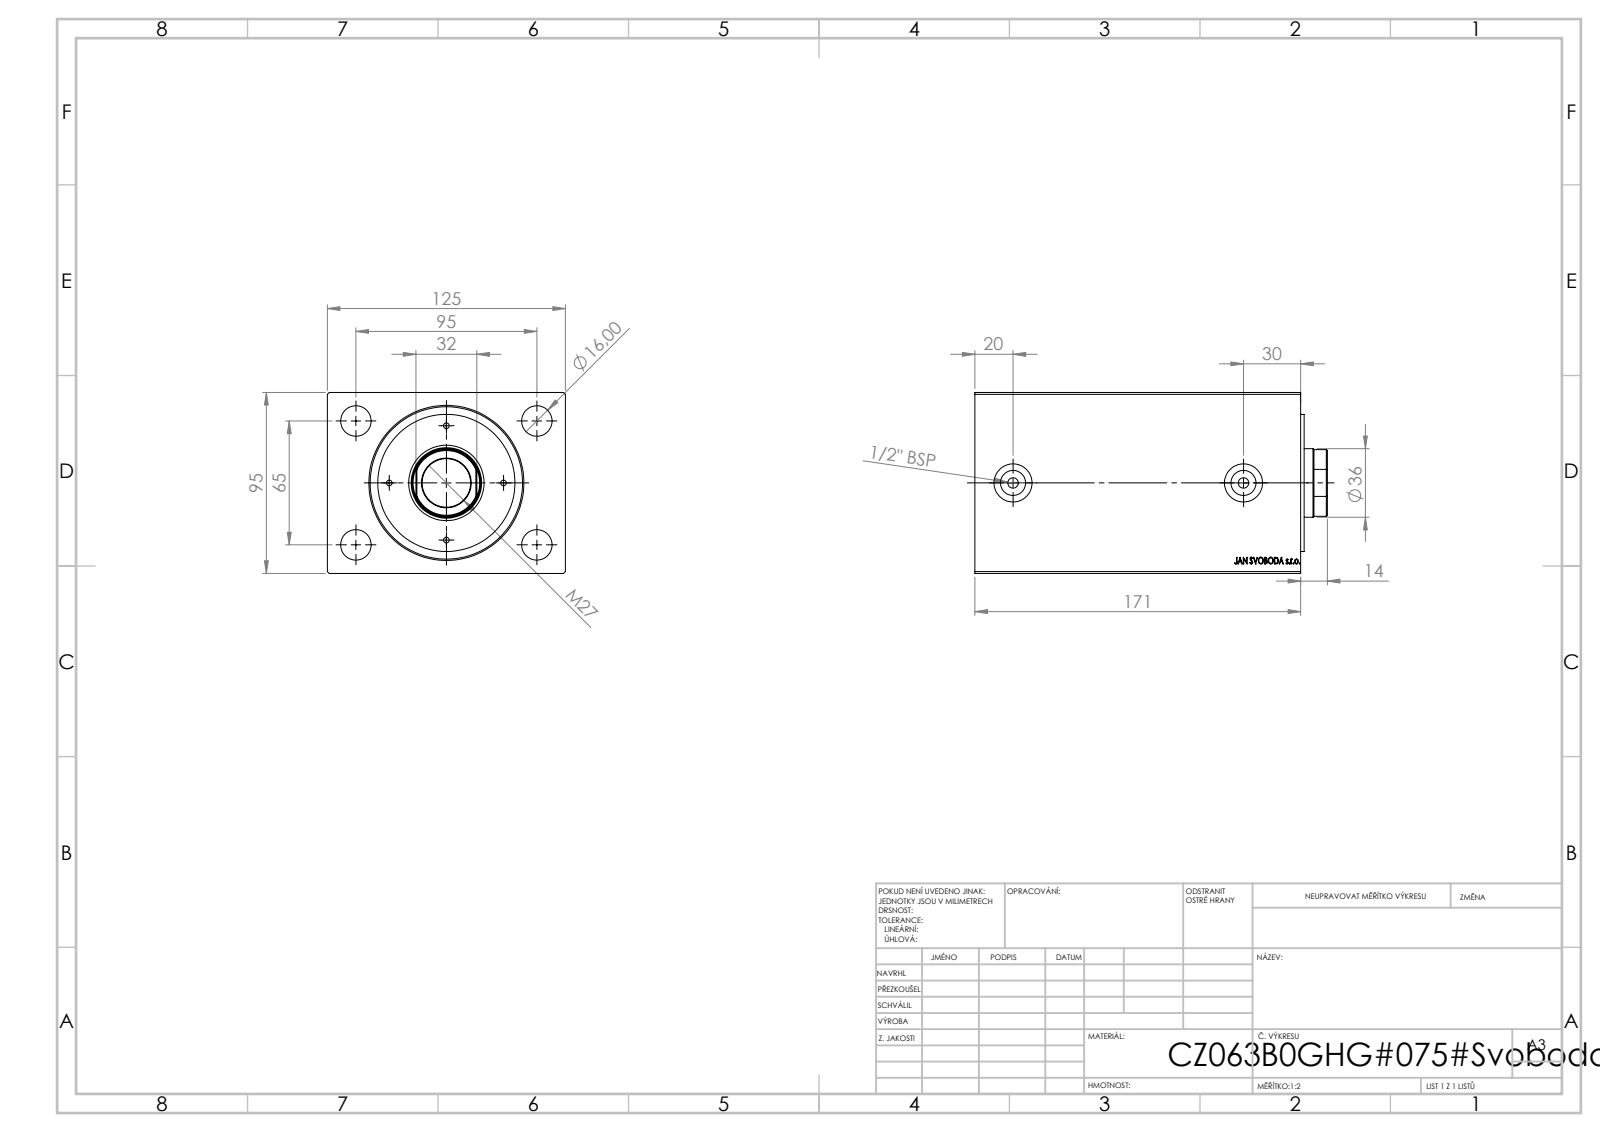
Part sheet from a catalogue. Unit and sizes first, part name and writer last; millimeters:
Units: millimetres
Overall size (bounding box): 185 × 125 × 95
Round holes (diameter × count): ⌀3 ×4, ⌀16 ×4, ⌀5.5 ×2, ⌀13.16 ×2, ⌀20 ×2, ⌀25.5 ×1, ⌀36 ×1, ⌀37 ×1, ⌀63 ×1, ⌀80 ×1
Round bosses / shafts (diameter × count): ⌀72 ×1
Partial cylindrical surfaces — rounded edges, fillets, slot ends (radius × count): R17.5 ×1
Main face-to-face distances: 95, 125, 171, 150.2, 20.8, 14, 1.8, 12.2, 138, 158.8
Hole centre spacings: 30, 36.91, 42.43, 47.57, 57.55, 78.5, 84.04, 60
Volume: 1 814 000 mm³ · Surface area: 187 028 mm²
Bodies: 3 solids, 874 faces (400 planar, 58 cylindrical, 416 other)
Part name (STEP PRODUCT): V500CZ_B_VC; V500CZ
STEP written by: SolidWorks 2019 (CONFIG_CONTROL_DESIGN)
